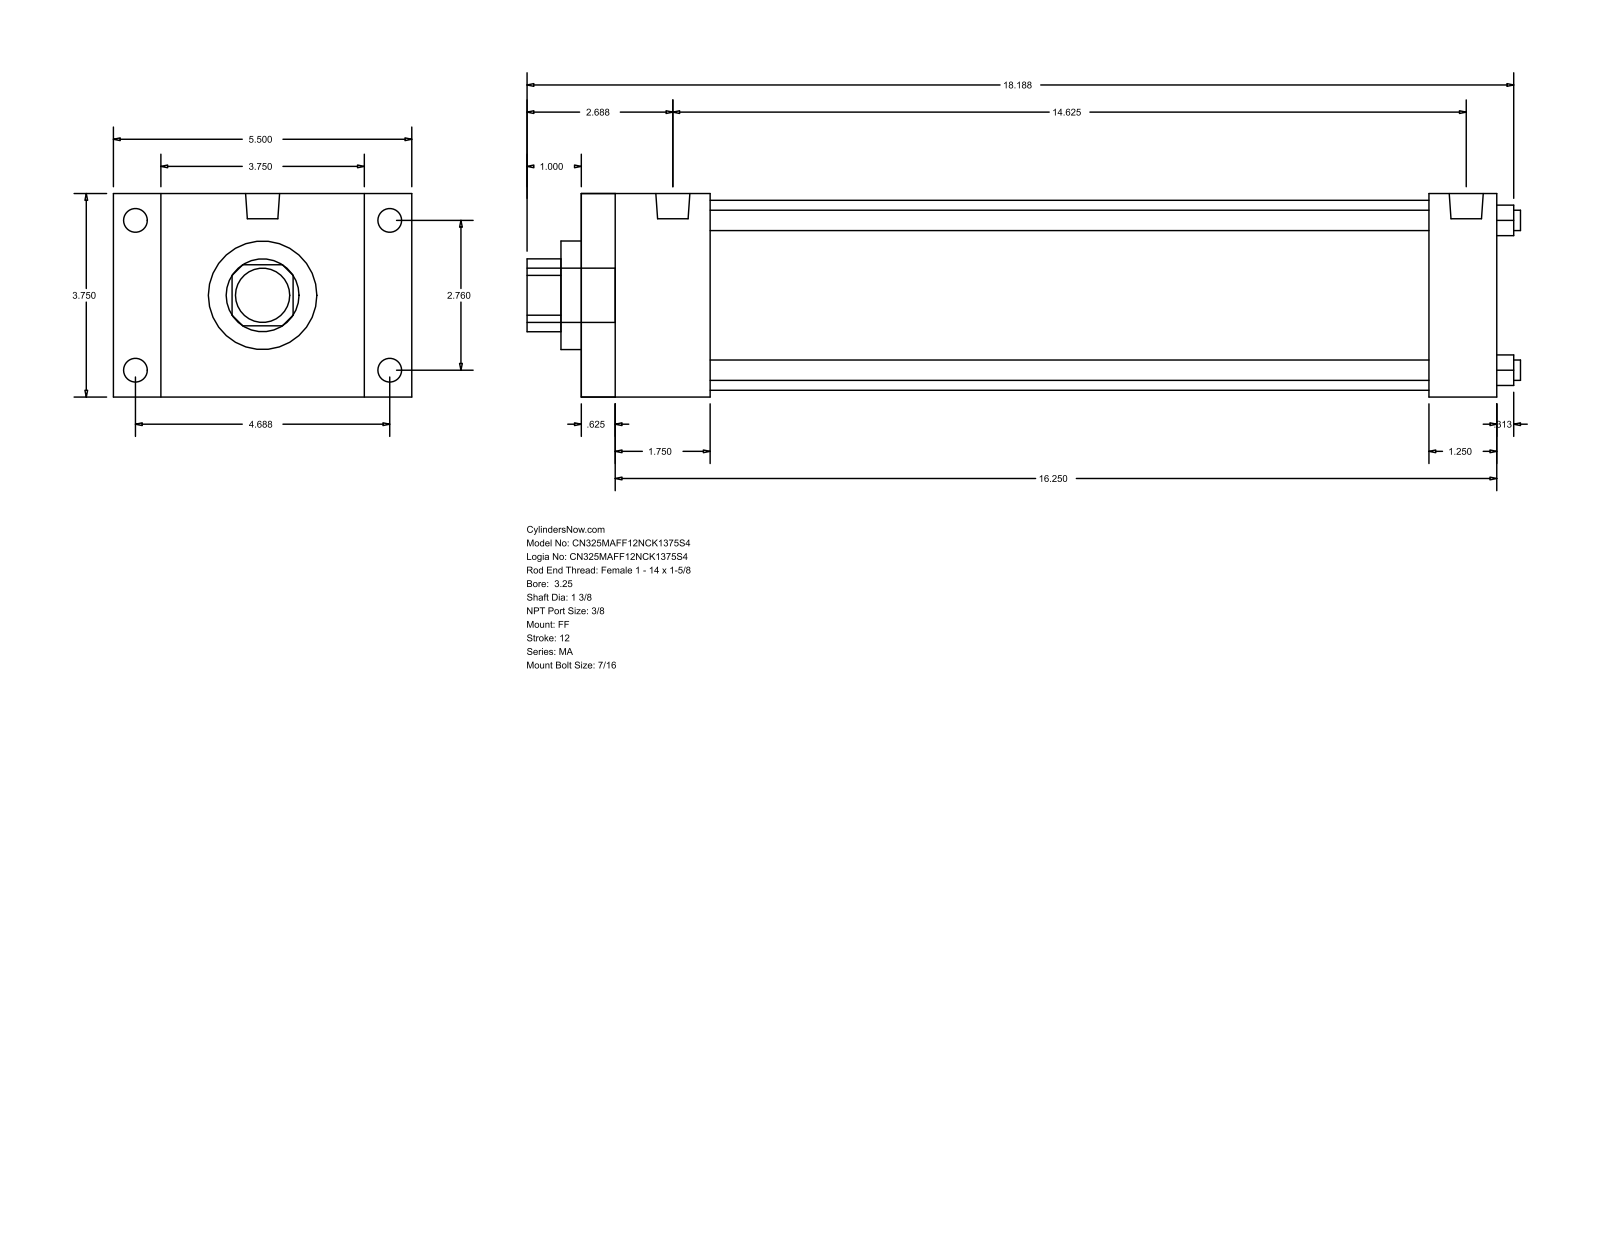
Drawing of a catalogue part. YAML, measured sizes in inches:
part_name: "MA_FF__0325_1.375"
step_written_by: "GSSL Pune (CONFIG_CONTROL_DESIGN)"
units: inches
bodies: {solids: 0, faces: 92, planar: 64, cylindrical: 28, other: 0}
overall_size: [18.313, 5.5, 3.75]
round_holes:
  - {diameter: 0.375, count: 4}
  - {diameter: 1.375, count: 1}
  - {diameter: 2, count: 1}
  - {diameter: 3.5, count: 1}
round_bosses_or_shafts:
  - {diameter: 0.437, count: 8}
  - {diameter: 0.627, count: 2}
  - {diameter: 1, count: 1}
partial_cylinders:
  - {radius: 0.672, count: 1}
face_to_face_distances: [3.75, 16.875, 0.625, 16.25, 0.875, 4.625, 2.375, 15.625, 1.75, 15]
hole_center_spacings: [1.952, 2.76, 3.903]
